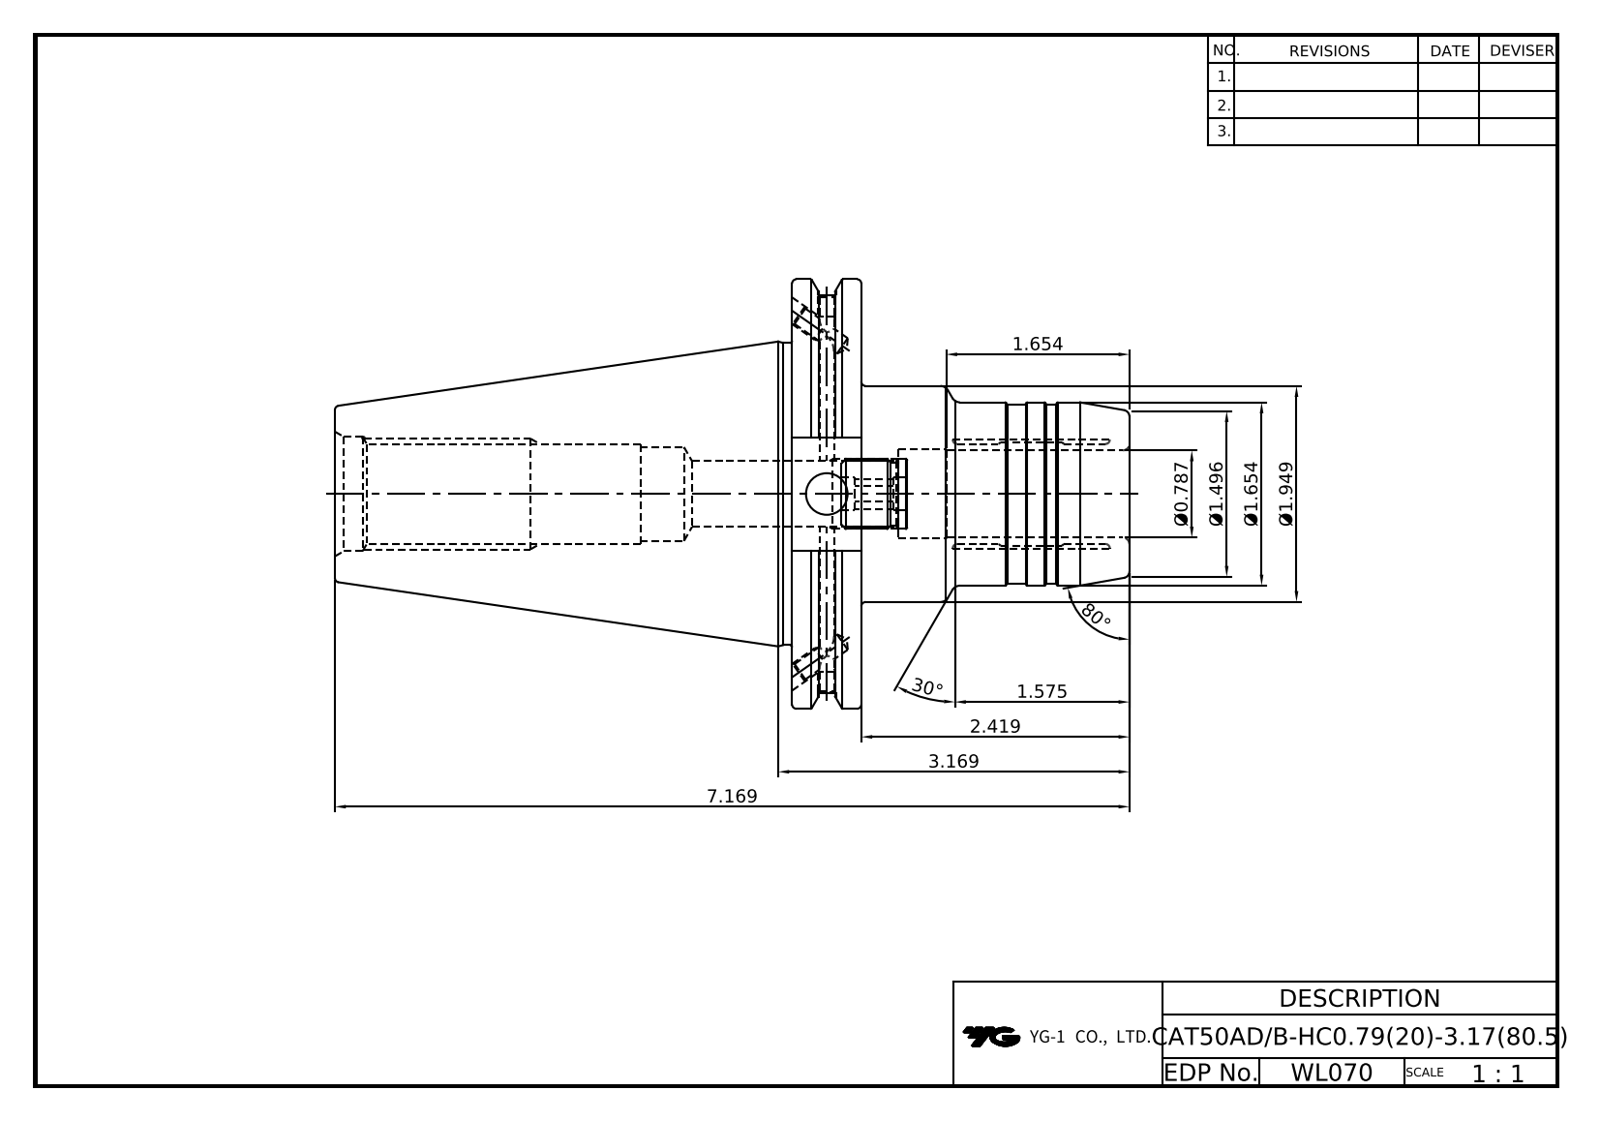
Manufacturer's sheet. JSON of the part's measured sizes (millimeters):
{"part_name": "LO-CAT50ADB-HC20-80.5", "step_written_by": "Autodesk Inventor 2022 (AUTOMOTIVE_DESIGN)", "units": "millimeters", "bodies": {"solids": 1, "faces": 106, "planar": 37, "cylindrical": 32, "other": 37}, "overall_size": [182.1, 98.42, 94.69], "volume_mm3": 402514, "surface_area_mm2": 55887, "round_holes": [[3.24, 2], [4.13, 2], [4.2, 2], [5, 2], [9.53, 1], [14.92, 1], [20, 1], [20.4, 1], [20.5, 1], [21.97, 1], [26.2, 1]], "round_bosses_or_shafts": [[98.42, 1], [91.29, 1], [69.25, 1], [49.5, 1], [42, 1], [41, 1]], "face_to_face_distances": [15.88, 77.33, 61.45, 104.77, 120.65, 182.1, 73.03, 25.9, 110.82, 6.05]}
